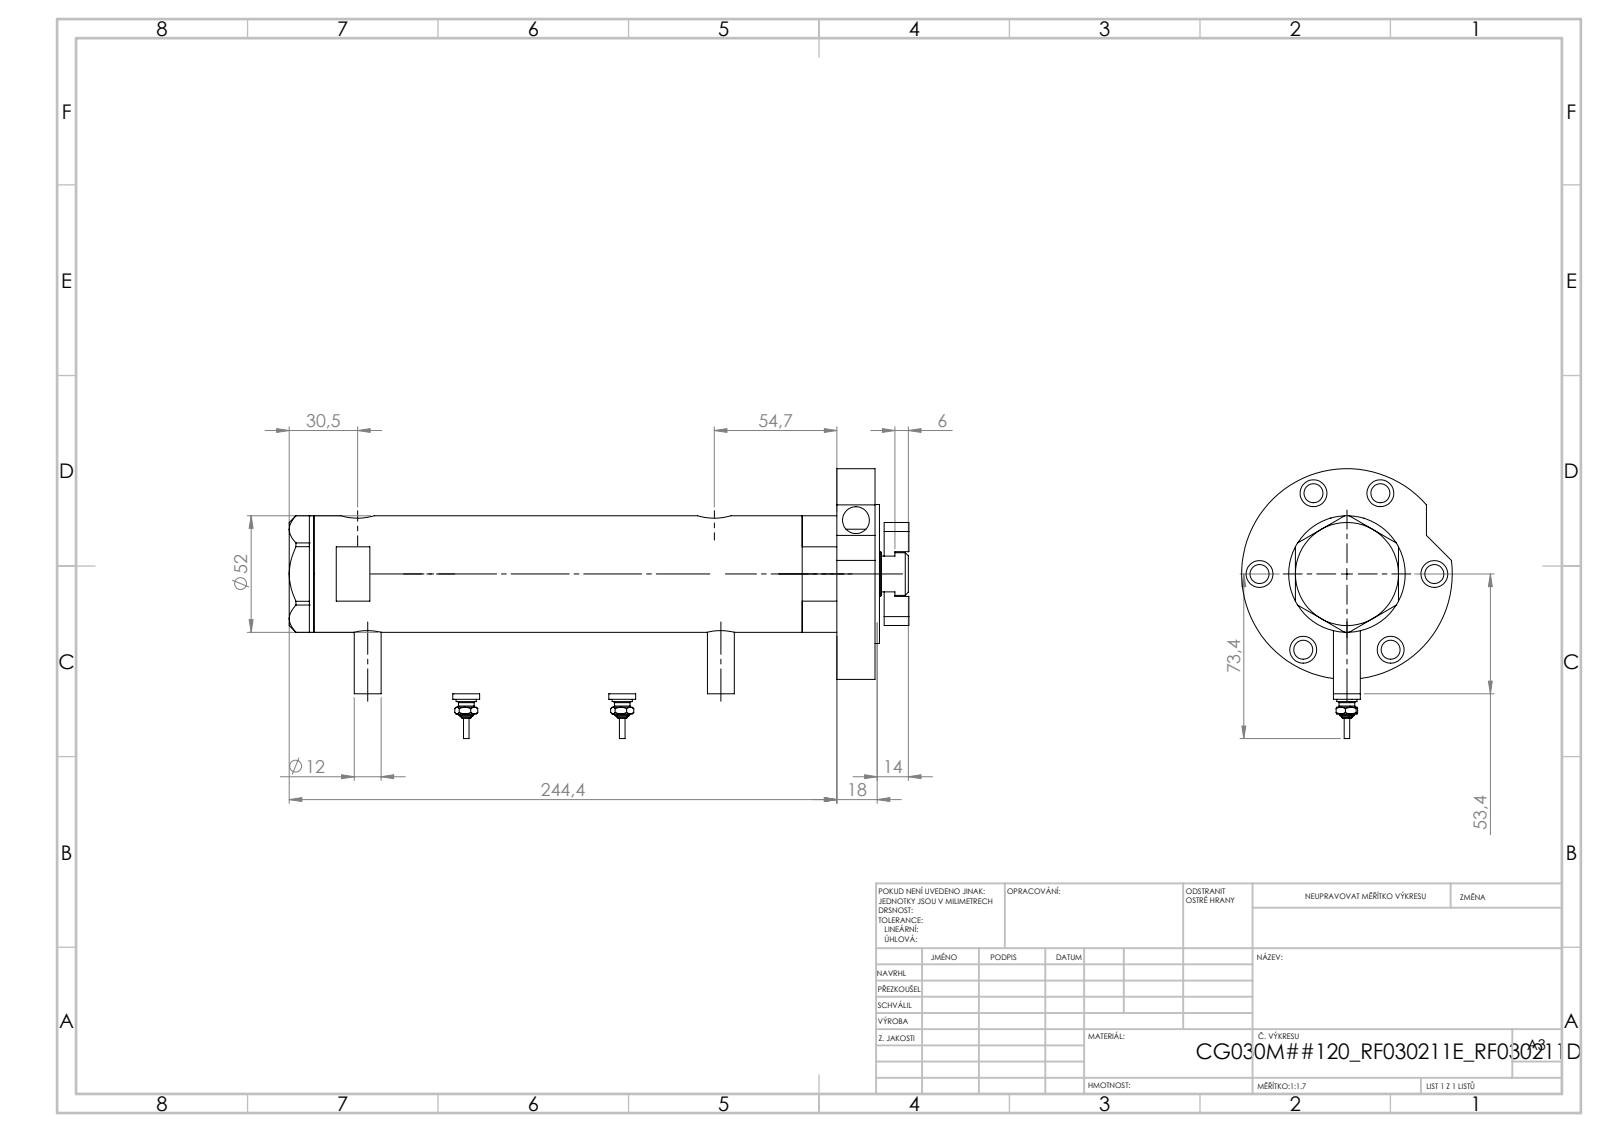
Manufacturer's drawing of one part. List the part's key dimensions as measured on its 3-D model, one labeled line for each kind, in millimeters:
Part name (STEP PRODUCT): V270CG_RF211D; V270CG_FRONT; V270CG_BACK; V270CG_MIDDLE (+3 more)
STEP written by: SolidWorks 2019 (CONFIG_CONTROL_DESIGN)
Units: millimetres
Bodies: 9 solids, 330 faces (130 planar, 126 cylindrical, 74 other)
Overall size (bounding box): 269.22 × 105.3 × 94
Volume: 564 186 mm³ · Surface area: 132 690 mm²
Round holes (diameter × count): ⌀12 ×7, ⌀8.5 ×6, ⌀5.1 ×4, ⌀9 ×4, ⌀5 ×2, ⌀9.73 ×2, ⌀12.5 ×2, ⌀15 ×2, ⌀6.5 ×1, ⌀20 ×1, ⌀21.5 ×1, ⌀30 ×1
Round bosses / shafts (diameter × count): ⌀12 ×3, ⌀9 ×2, ⌀7 ×2, ⌀4.34 ×2, ⌀2.4 ×2, ⌀94 ×1, ⌀62 ×1, ⌀52 ×1
Main face-to-face distances: 17, 225.44, 242.44, 2, 244.44, 11, 19, 23.8, 201.64, 218.64
Hole centre spacings: 39, 16.74, 37.57, 46.81, 2.9, 4.5, 10, 22.37
